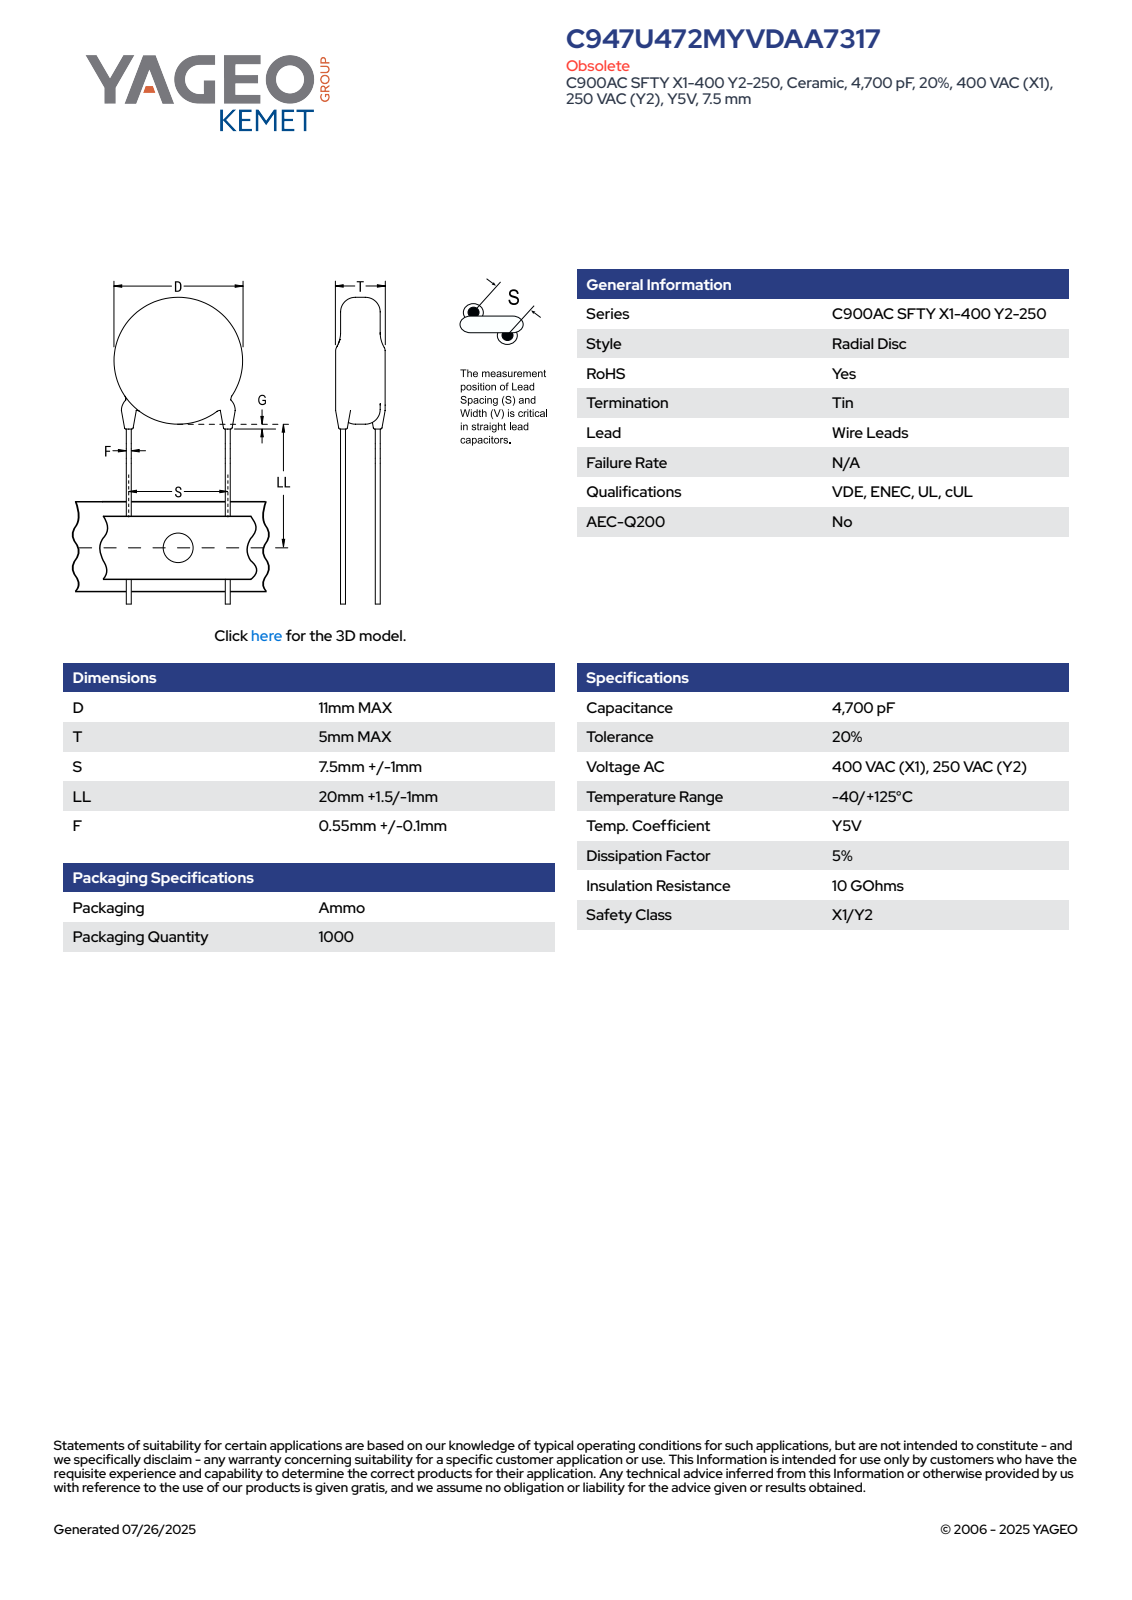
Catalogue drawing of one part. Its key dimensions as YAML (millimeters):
part_name: "CCD_STC900_D11T5S7.5LL21.5F0.65G3"
step_written_by: "SolidWorks 2014 (AUTOMOTIVE_DESIGN)"
units: millimeters
bodies: {solids: 4, faces: 83, planar: 61, cylindrical: 6, other: 16}
overall_size: [32.5, 11, 5]
volume: 477
surface_area: 435
round_bosses_or_shafts:
  - {diameter: 0.65, count: 2}
  - {diameter: 11, count: 1}
face_to_face_distances: [5, 1.27, 27.63, 26.36, 0.35, 1.03, 5.19, 0.79, 3.77, 3.92]
